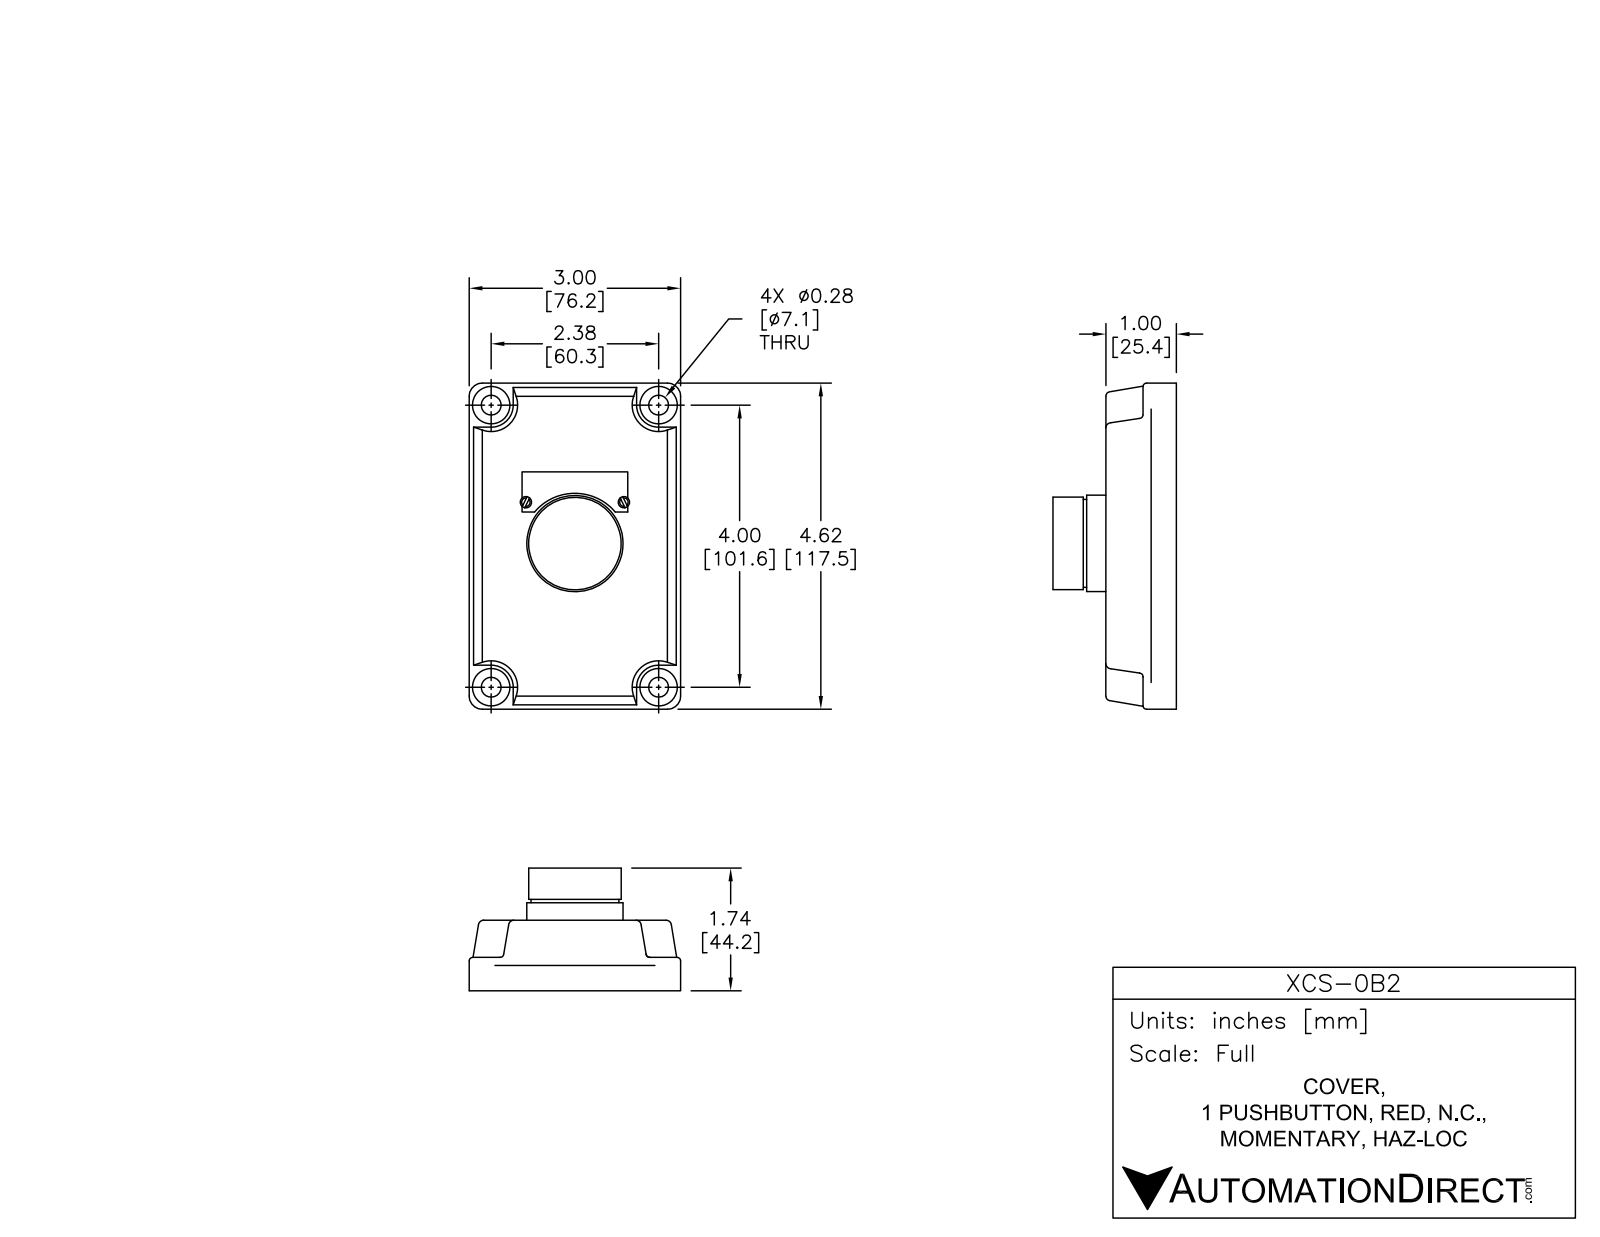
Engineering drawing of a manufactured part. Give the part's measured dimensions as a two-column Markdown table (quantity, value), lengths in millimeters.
| quantity | value |
| --- | --- |
| part name | XCS-0B2 |
| STEP written by | SolidWorks 2015 (AUTOMOTIVE_DESIGN) |
| units | millimeters |
| bodies | 10 solids, 470 faces (166 planar, 171 cylindrical, 133 other) |
| overall size | 117.6 × 81.1 × 78.74 |
| volume | 207 620 mm³ |
| surface area | 55 537 mm² |
| round holes (diameter × count) | 6.65 × 4, 6.86 × 4, 28.5 × 1 |
| round bosses / shafts (diameter × count) | 3.3 × 6, 11.6 × 4, 6.35 × 4, 35 × 1, 32.06 × 1, 26.25 × 1 |
| partial cylindrical surfaces (radius × count) | 0.25 × 28, 1.27 × 10, 0.51 × 8, 1.4 × 8, 3 × 8, 2.38 × 4, 2.54 × 4, 9.65 × 4 |
| main face-to-face distances | 13.34, 12.7, 26.04, 11.3, 24, 37.34, 17.5, 6.5, 4.8, 30.84 |
| hole center spacings | 59.11, 10.2, 20.4, 60.46, 101.6, 118.23, 10.13, 10.18 |
